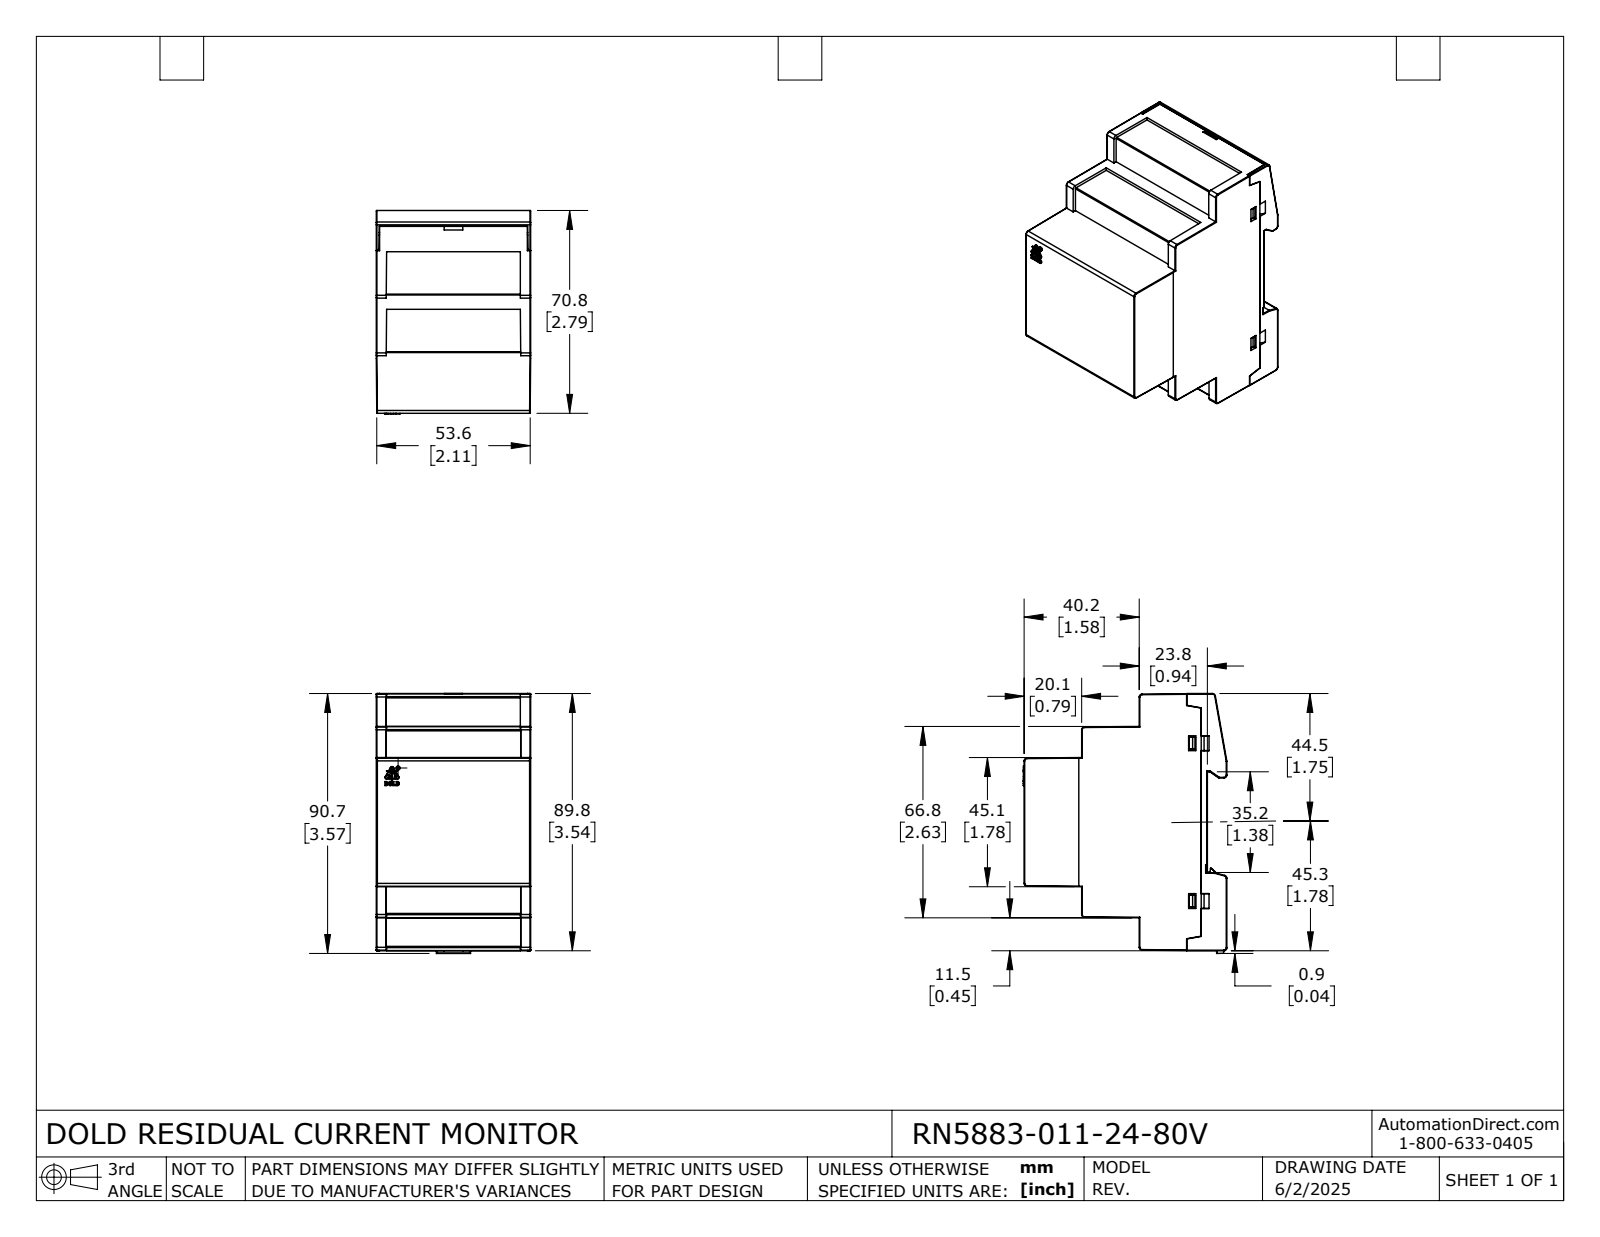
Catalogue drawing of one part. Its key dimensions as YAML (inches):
part_name: "RN5883-011-24-80V"
step_written_by: "SolidWorks 2024 (AUTOMOTIVE_DESIGN)"
units: inches
bodies: {solids: 13, faces: 1307, planar: 1035, cylindrical: 186, other: 86}
overall_size: [3.572, 2.797, 2.122]
volume: 14.21
surface_area: 80.85
round_holes:
  - {diameter: 0.049, count: 1}
round_bosses_or_shafts:
  - {diameter: 0.098, count: 6}
  - {diameter: 0.157, count: 4}
  - {diameter: 0.181, count: 1}
  - {diameter: 0.053, count: 1}
partial_cylinders:
  - {radius: 0.008, count: 44}
  - {radius: 0.004, count: 19}
  - {radius: 0.039, count: 18}
  - {radius: 0.02, count: 11}
  - {radius: 0.005, count: 6}
  - {radius: 0.004, count: 4}
  - {radius: 0.012, count: 4}
  - {radius: 0.021, count: 3}
face_to_face_distances: [0.136, 2.122, 1.986, 0.063, 0.073, 2.049, 1.913, 0.041, 2.435, 0.085]
